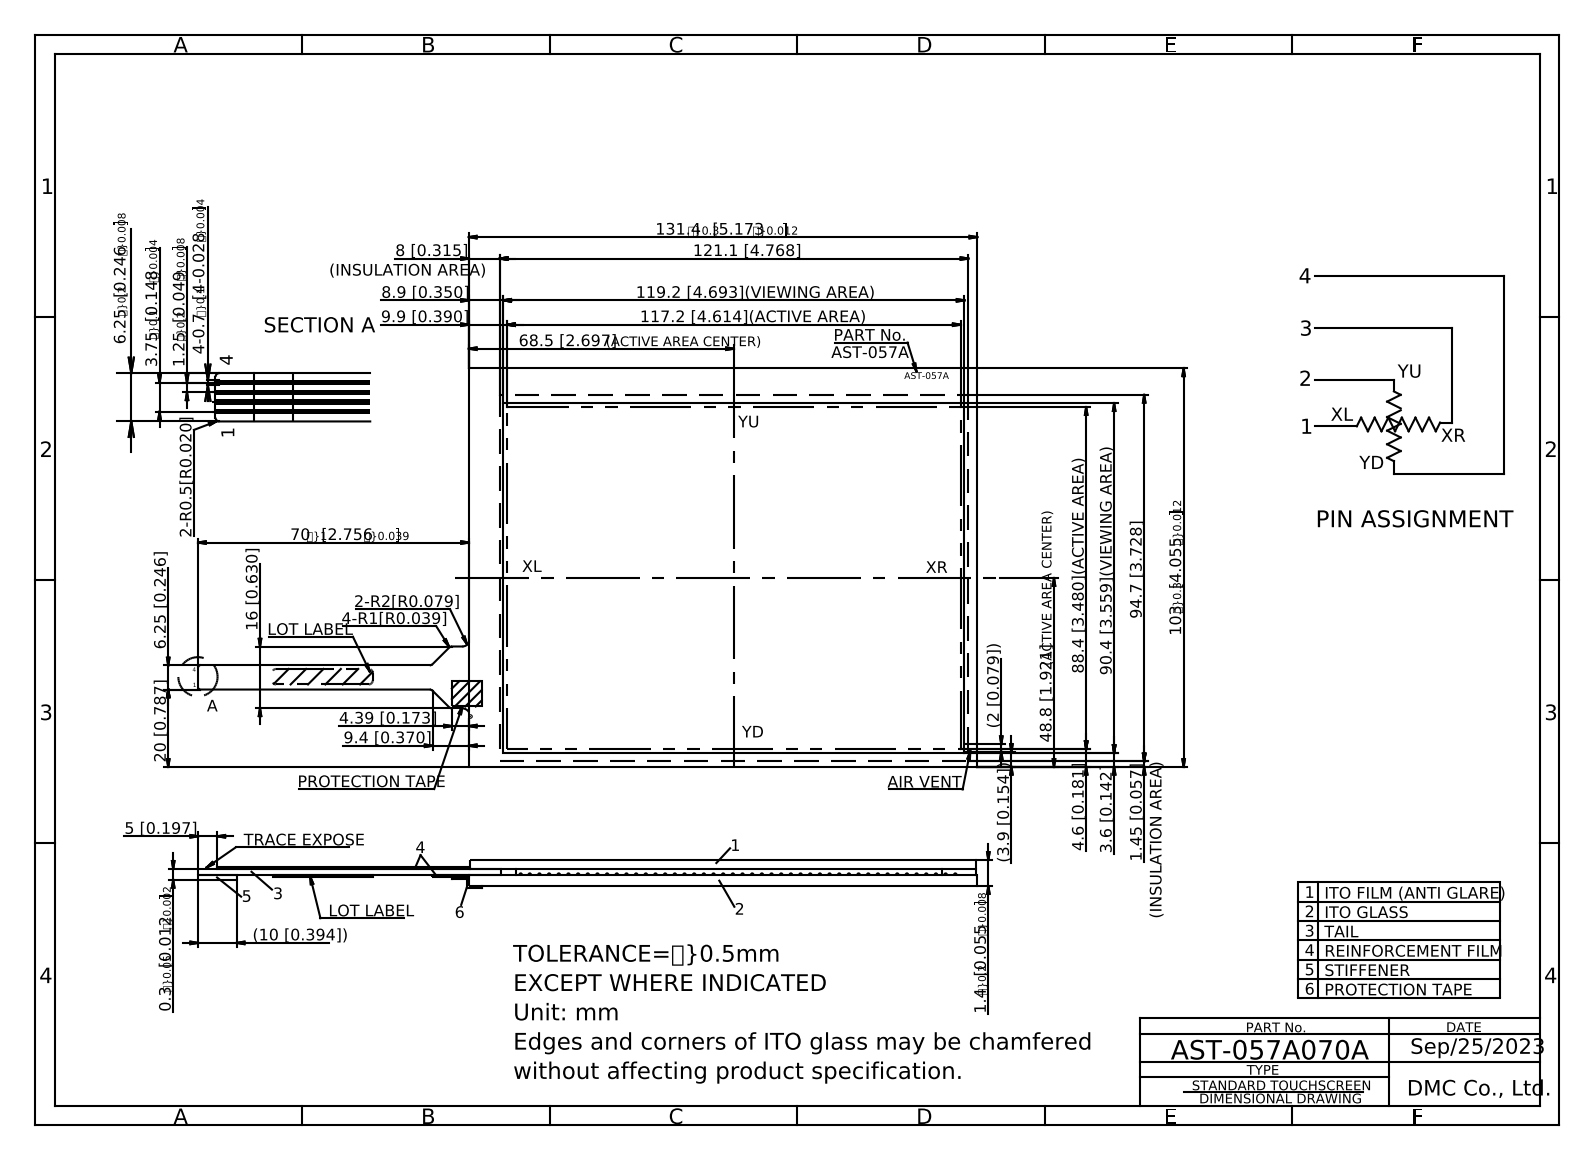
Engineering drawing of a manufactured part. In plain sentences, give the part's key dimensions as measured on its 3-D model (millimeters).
The part is named "AST-057A070A". Its 3-D file was written by "Autodesk Inventor 2020 (CONFIG_CONTROL_DESIGN)". It is 1 solid with 51 faces: 45 planar, 6 cylindrical and 0 other. Overall it measures 227.68 by 144.2 by 1.4 millimeters. Its volume is 18 972 cubic millimeters and its surface area 28 838 square millimeters. Partial cylindrical surfaces (rounded edges, fillets, slot ends): 4 of radius 1, 2 of radius 0.5. The main face-to-face distances are 1.4, 1.2, 1.1, 1.3, 103, 131.4, 0.8, 0.4, 0.5, 0.6.
